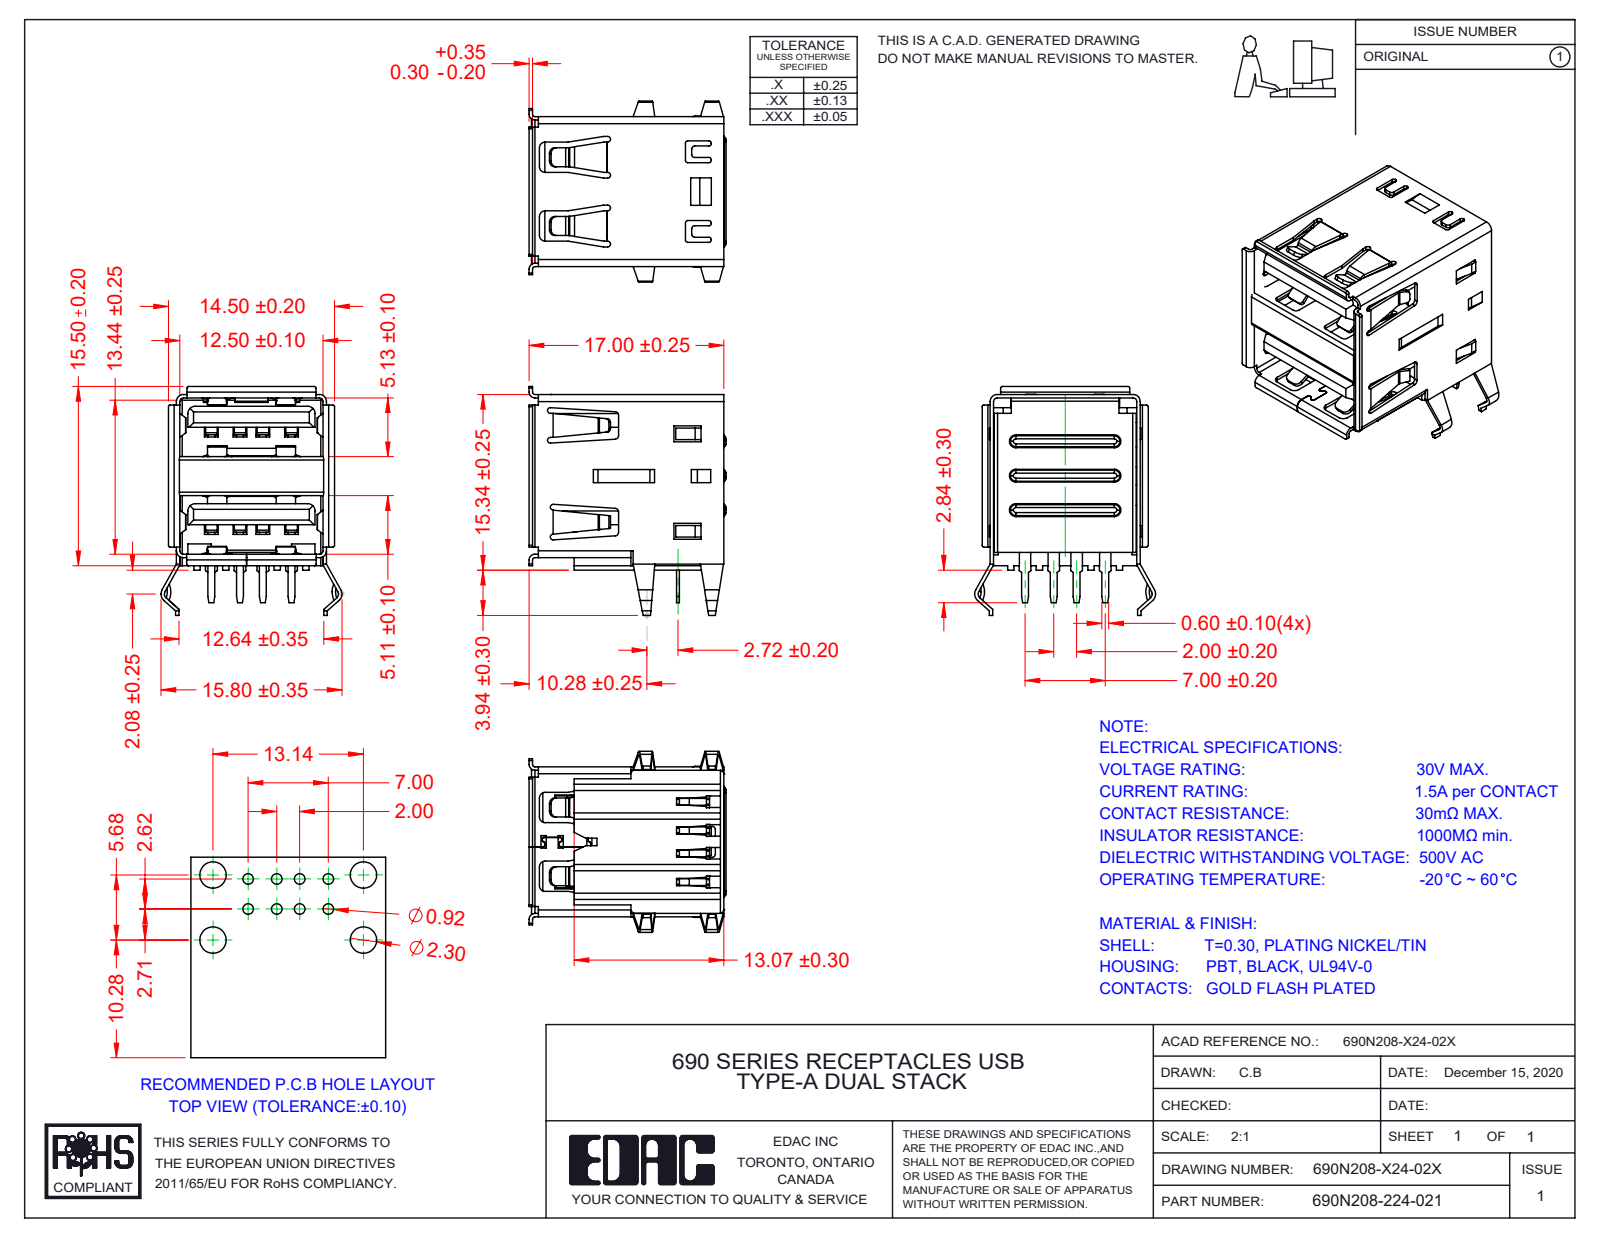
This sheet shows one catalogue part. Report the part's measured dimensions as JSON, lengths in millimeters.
{"part_name": "Contact Upper 690N208-X24-02X; Shell 2 690N208-X24-02X; Contact Lower 690N208-X24-02X; 690N208-124-021 (+2 more)", "step_written_by": "SolidWorks 2020 (AUTOMOTIVE_DESIGN)", "units": "millimeters", "bodies": {"solids": 11, "faces": 1766, "planar": 1394, "cylindrical": 329, "other": 43}, "overall_size": [19.98, 17.2, 15.8], "volume_mm3": 1554, "surface_area_mm2": 5527, "partial_cylinders_radius": [[0.25, 39], [0.2, 31], [0.5, 25], [0.3, 23], [0.1, 14], [0.15, 9], [0.4, 7], [0.18, 4]], "face_to_face_distances": [12.8, 0.7, 12.5, 8.5, 4.5, 5.41, 2.5, 1, 13.1, 13.94]}
